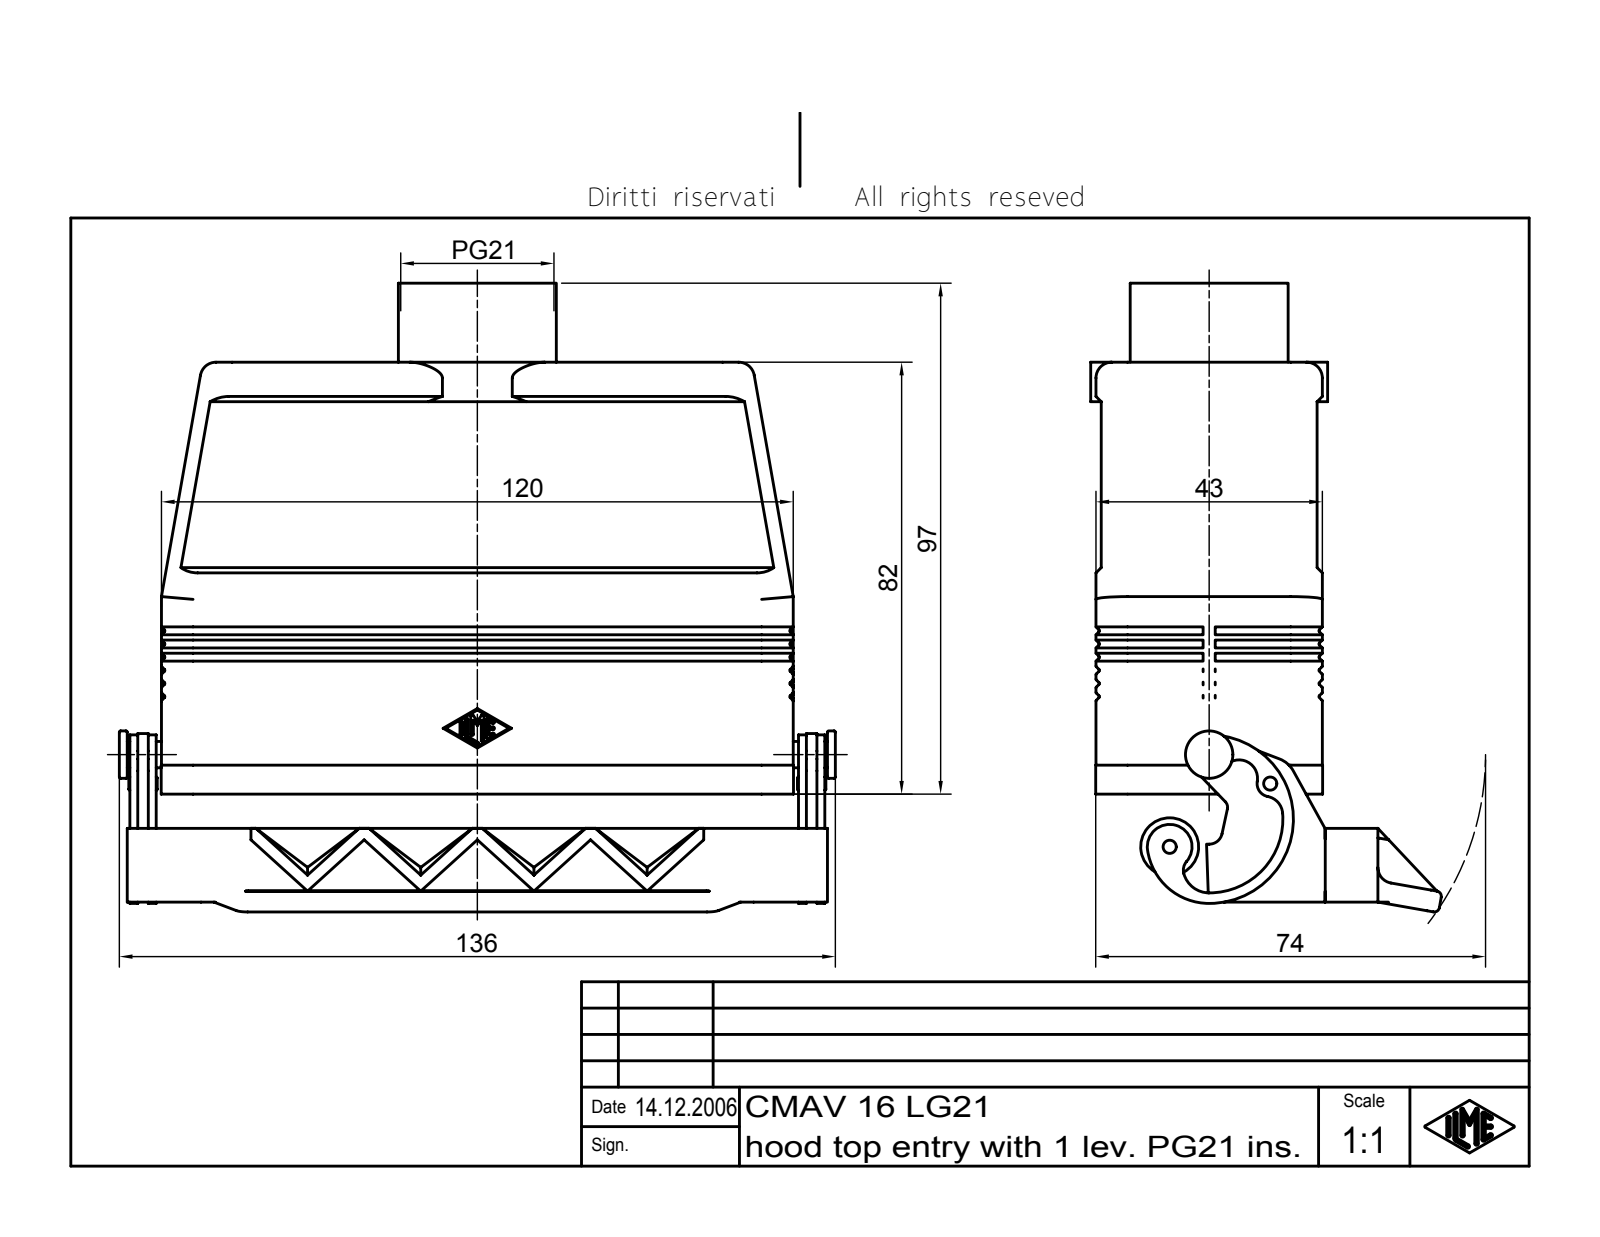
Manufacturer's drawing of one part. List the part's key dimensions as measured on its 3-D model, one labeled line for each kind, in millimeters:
Part name (STEP PRODUCT): CMAV 16 LG21
STEP written by: Autodesk Inventor 7 (AUTOMOTIVE_DESIGN)
Units: millimetres
Bodies: 1 solid, 960 faces (235 planar, 324 cylindrical, 401 other)
Overall size (bounding box): 136 × 119.37 × 66.59
Volume: 125 339 mm³ · Surface area: 74 469 mm²
Round holes (diameter × count): ⌀2.5 ×1, ⌀24.78 ×1, ⌀26.78 ×1
Round bosses / shafts (diameter × count): ⌀45 ×1, ⌀30 ×1, ⌀11 ×1, ⌀9 ×1, ⌀5 ×1, ⌀3.1 ×1, ⌀2 ×1
Partial cylindrical surfaces — rounded edges, fillets, slot ends (radius × count): R0.2 ×52, R0.25 ×32, R2.5 ×9, R6 ×8, R3 ×7, R1 ×6, R2.45 ×4, R6.05 ×4
Main face-to-face distances: 3.45, 3.5, 39.55, 39.5, 36.05, 36, 36.1, 2.5, 2.45, 1
